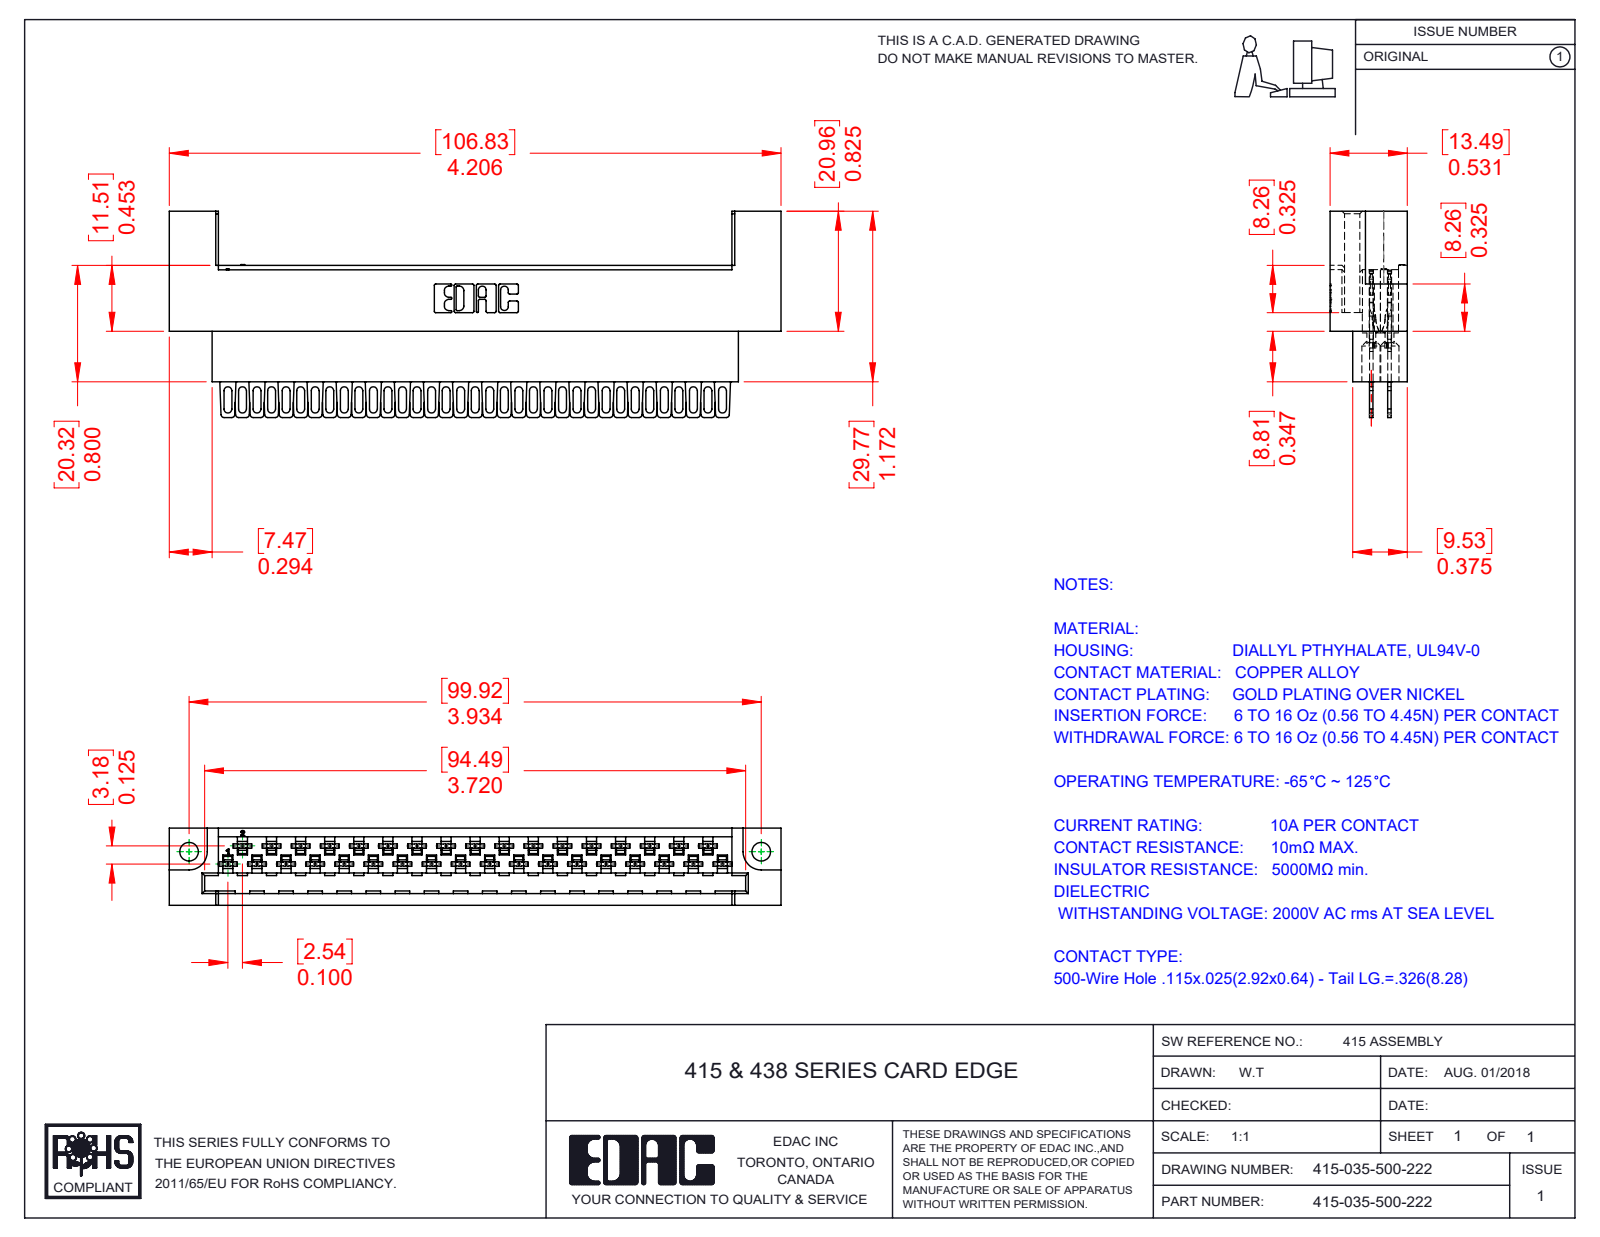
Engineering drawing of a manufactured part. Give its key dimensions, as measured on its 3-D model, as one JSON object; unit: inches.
{"part_name": "516-290-001_500; 415-035-500-222; 415-210-001_415-210-035-222", "step_written_by": "SolidWorks 2016 (CONFIG_CONTROL_DESIGN)", "units": "inches", "bodies": {"solids": 36, "faces": 3730, "planar": 2332, "cylindrical": 1061, "other": 337}, "overall_size": [4.206, 1.417, 0.531], "volume_in3": 1.126, "surface_area_in2": 36.6, "round_holes": [[0.05, 35], [0.13, 35], [0.128, 2]], "partial_cylinders_radius": [[0.012, 140], [0.022, 140], [0.007, 70], [0.008, 70], [0.016, 70], [0.02, 70], [0.027, 70], [0.08, 70]], "face_to_face_distances": [0.125, 0.024, 0.531, 0.295, 0.05, 0.074, 0.26, 0.271, 0.236, 0.111], "hole_center_spacings": [0.2, 0.4, 0.6, 0.8, 1, 1.2, 1.4, 0.1]}
